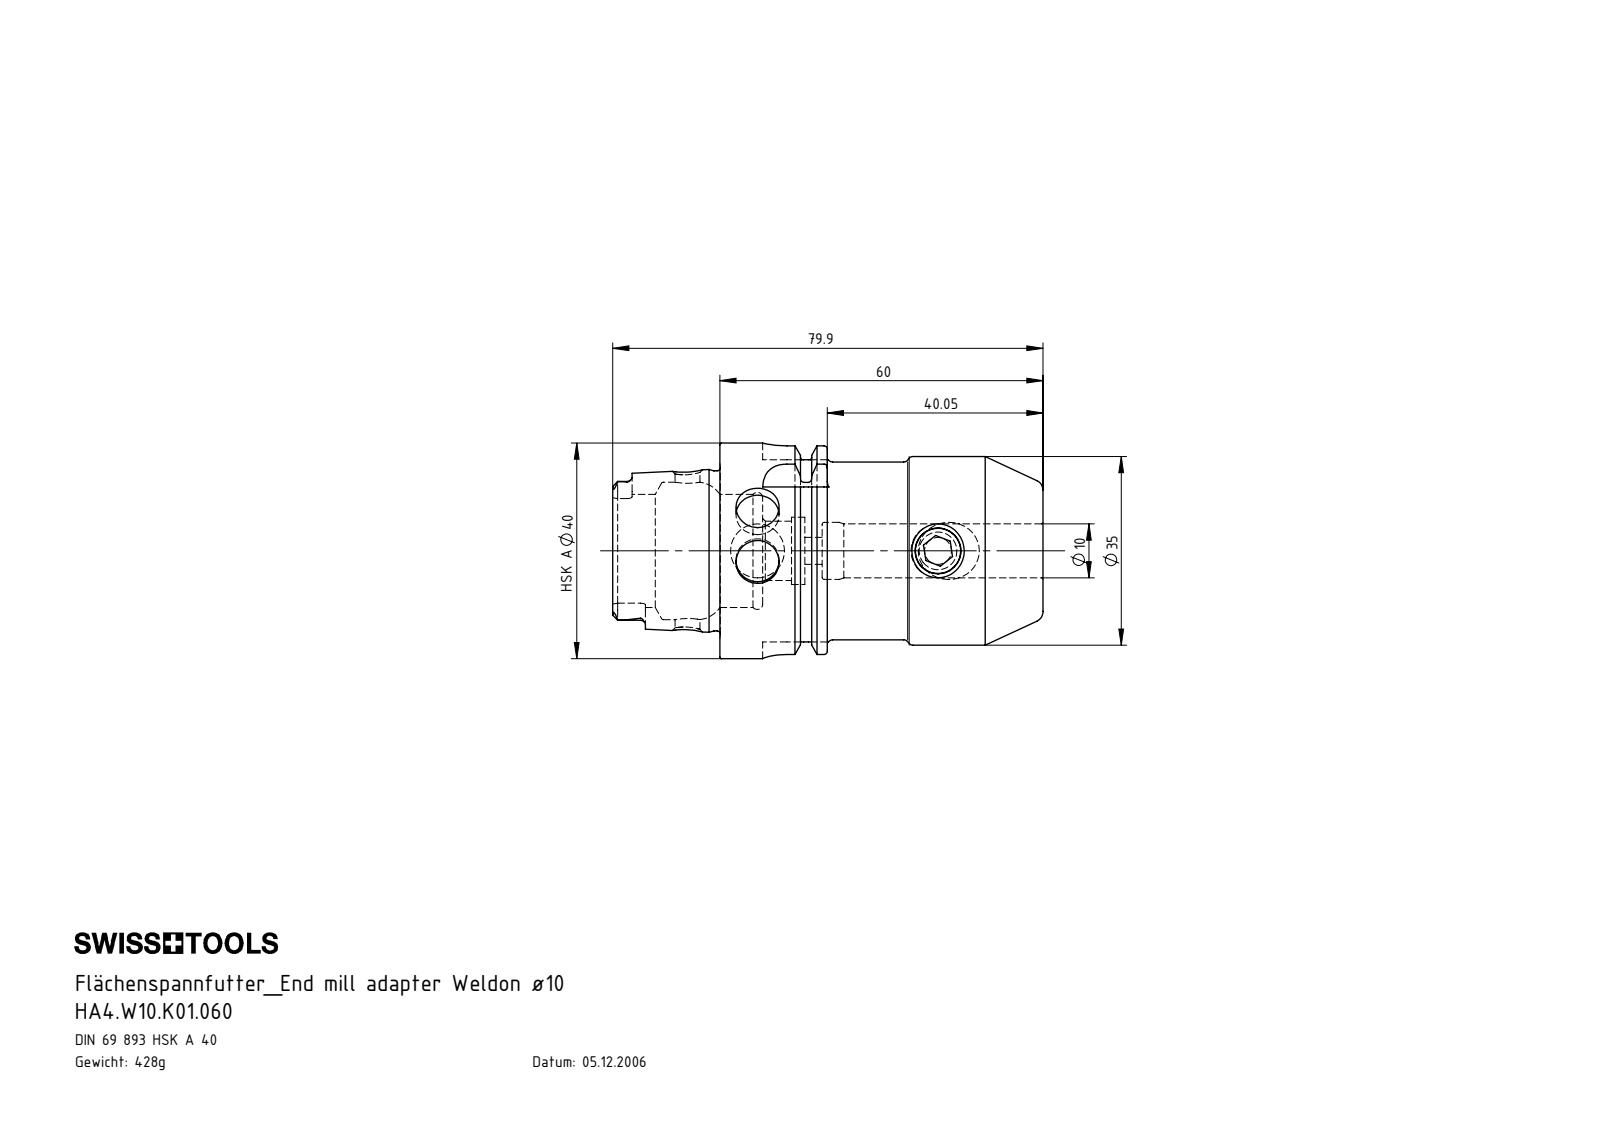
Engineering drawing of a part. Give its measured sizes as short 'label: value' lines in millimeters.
name: HA4.W10.K01.060; W10-ER1.001.012; HA4-W10.K01.060_B_Fertigbearbeitung
written by: SolidWorks 2017 (CONFIG_CONTROL_DESIGN)
unit: mm
bodies: 2 solids, 205 faces (58 planar, 60 cylindrical, 87 other)
size: 79.9 × 40 × 40
volume: 54 582 mm³; area: 15 729 mm²
holes: 2× ⌀8, 2× ⌀10, 1× ⌀4.6, 1× ⌀5, 1× ⌀8.5, 1× ⌀10.6, 1× ⌀11, 1× ⌀12.5, 1× ⌀21, 1× ⌀25.5
bosses: 1× ⌀40, 1× ⌀35, 1× ⌀34.75, 1× ⌀33, 1× ⌀29.71, 1× ⌀10
rounds: 6× R0.9, 4× R1.88, 4× R4.5
face distances: 60, 7.95, 52.05, 19.95, 12, 40.05, 19.9, 27.85, 39.85, 79.9
hole spacings: 33.5
